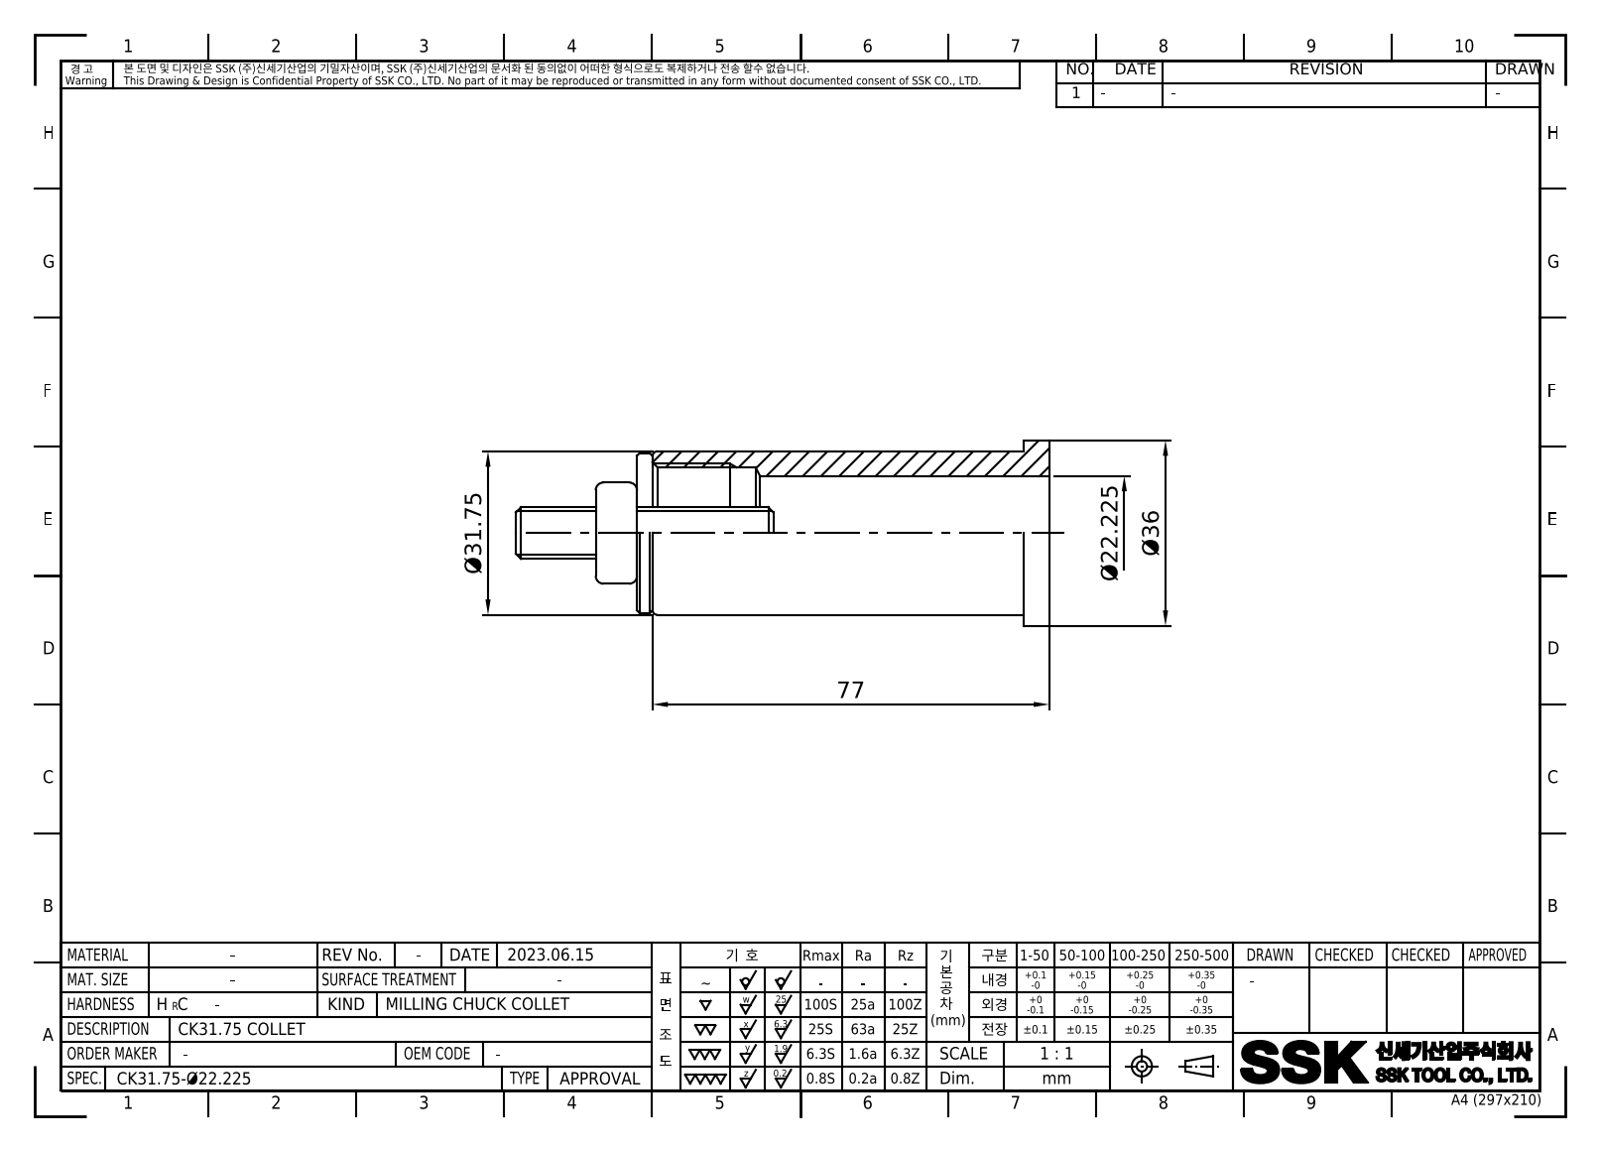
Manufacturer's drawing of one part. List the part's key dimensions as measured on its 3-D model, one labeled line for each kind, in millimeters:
Part name (STEP PRODUCT): LO-CK31.75-22.225
STEP written by: Autodesk Inventor 2022 (AUTOMOTIVE_DESIGN)
Units: millimetres
Bodies: 1 solid, 8 faces (3 planar, 4 cylindrical, 1 other)
Overall size (bounding box): 77 × 36 × 36
Volume: 29 811 mm³ · Surface area: 14 535 mm²
Round holes (diameter × count): ⌀22.23 ×1, ⌀25.38 ×1
Round bosses / shafts (diameter × count): ⌀36 ×1, ⌀31.75 ×1
Main face-to-face distances: 77, 72, 5
